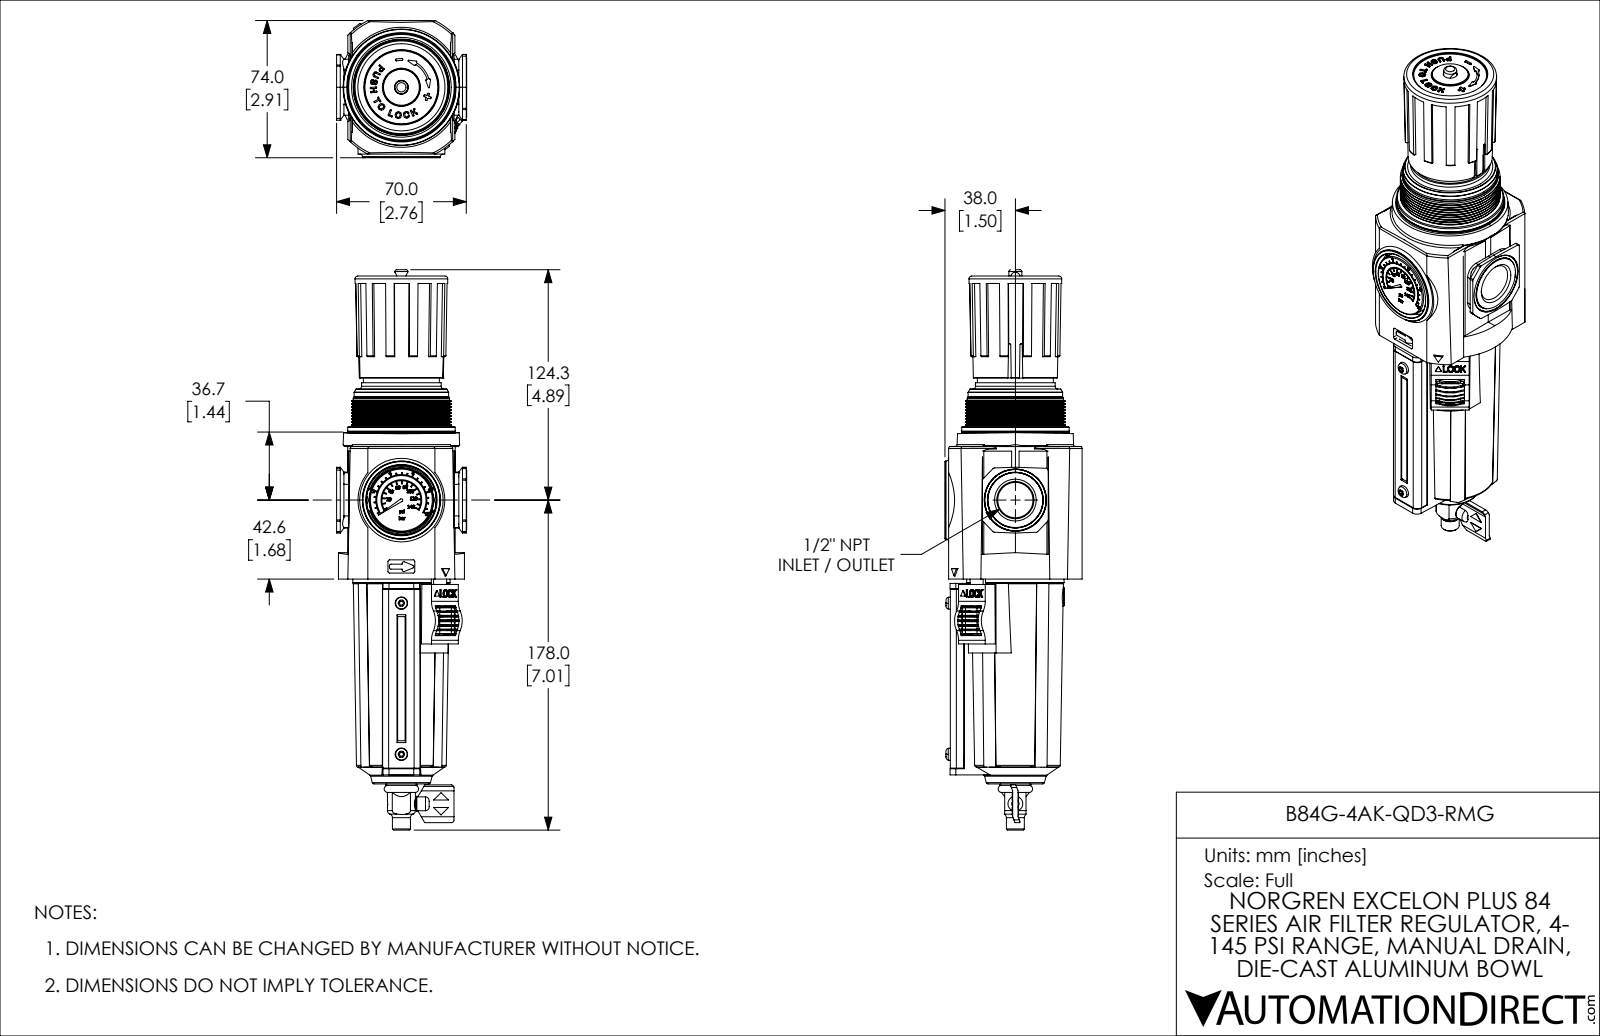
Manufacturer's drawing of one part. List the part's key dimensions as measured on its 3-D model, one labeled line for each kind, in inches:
Part name (STEP PRODUCT): B84G-4AK-QD3-RMG
STEP written by: SolidWorks 2021 (CONFIG_CONTROL_DESIGN)
Units: inches
Bodies: 9 solids, 2693 faces (980 planar, 1218 cylindrical, 495 other)
Overall size (bounding box): 11.9 × 2.913 × 2.766
Volume: 46.48 in³ · Surface area: 225.7 in²
Round holes (diameter × count): ⌀0.112 ×2, ⌀0.177 ×2, ⌀0.059 ×1, ⌀0.123 ×1, ⌀0.126 ×1, ⌀0.197 ×1, ⌀0.236 ×1, ⌀0.25 ×1, ⌀0.374 ×1, ⌀0.633 ×1, ⌀1.319 ×1, ⌀2.323 ×1
Round bosses / shafts (diameter × count): ⌀0.299 ×2, ⌀0.213 ×2, ⌀0.157 ×2, ⌀2.283 ×1, ⌀2.122 ×1, ⌀2.119 ×1, ⌀2.067 ×1, ⌀2.047 ×1
Partial cylindrical surfaces — rounded edges, fillets, slot ends (radius × count): R0.039 ×37, R0.028 ×28, R0.012 ×27, R0.02 ×23, R0.01 ×18, R0.047 ×18, R0.03 ×16, R0.004 ×14
Main face-to-face distances: 2.719, 2.323, 2.457, 0.364, 2.354, 0.622, 0.512, 0.134, 2.096, 1.732
Hole centre spacings: 0.856, 2.685, 5.121, 1.713, 2.504, 2.545, 5.049, 11.189
